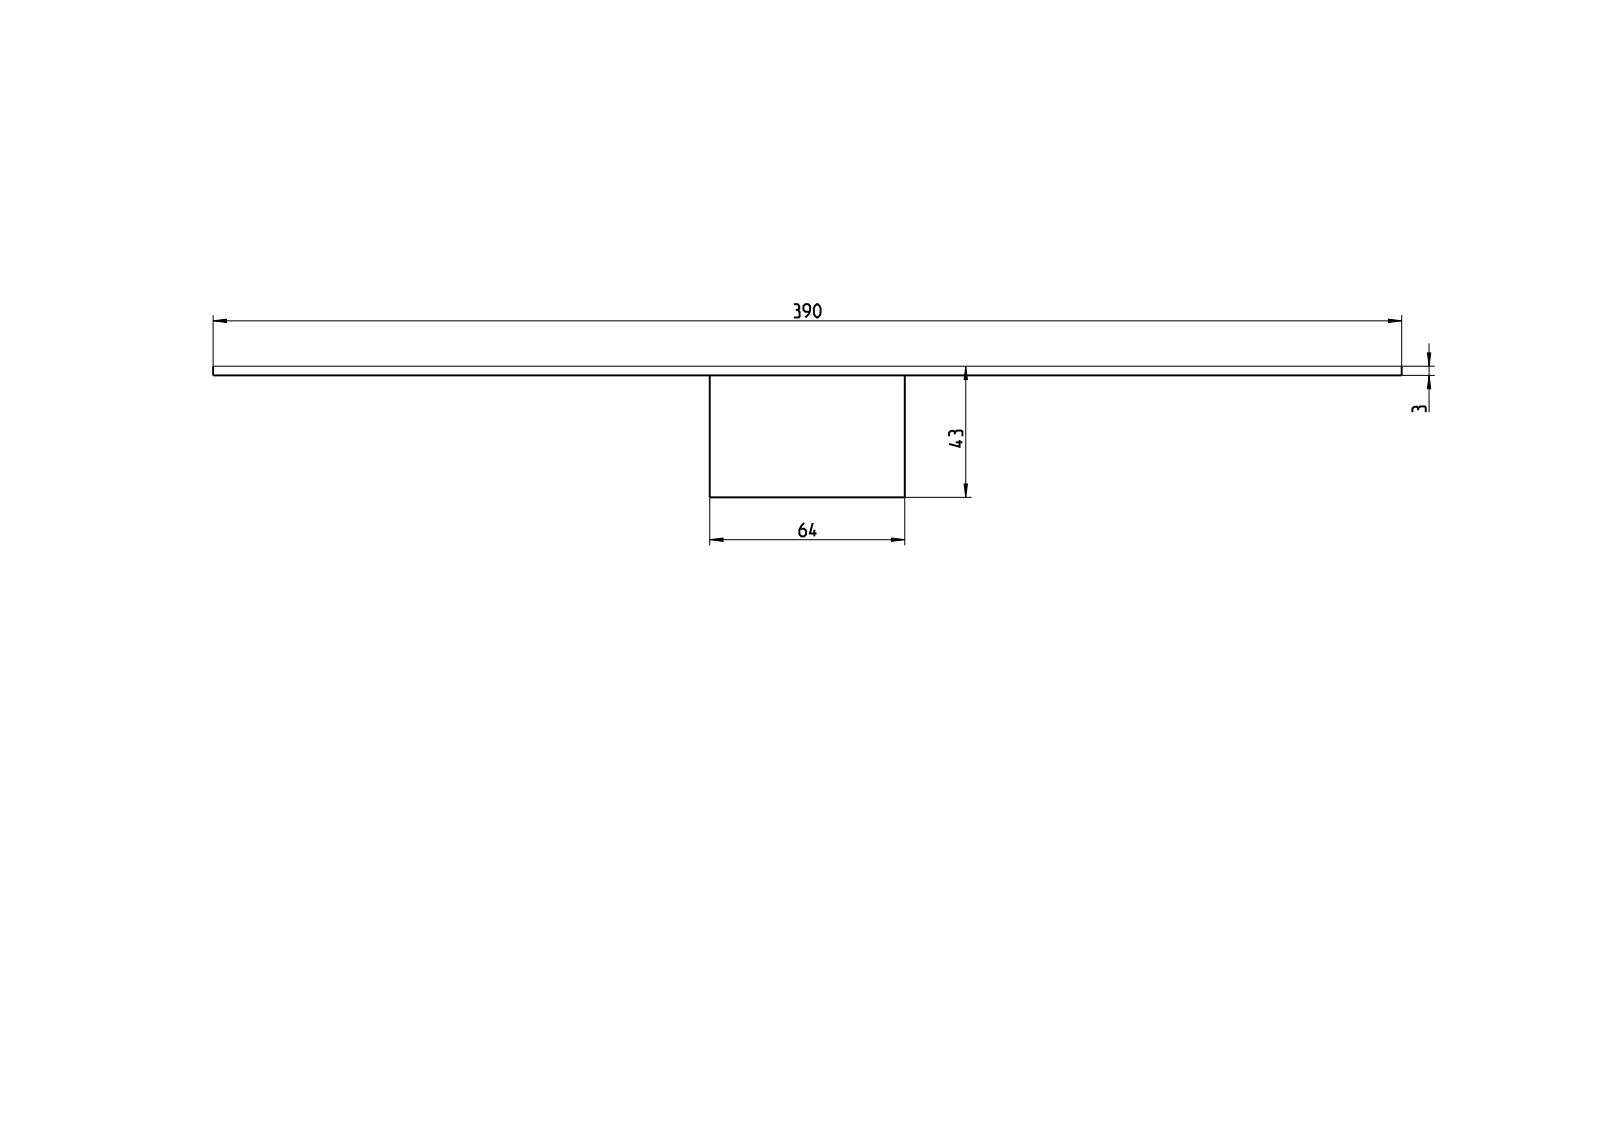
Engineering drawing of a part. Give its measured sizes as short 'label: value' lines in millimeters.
name: T-01191; AUSLASS; BKG4002LA_ASM
written by: CREO PARAMETRIC BY PTC INC, 2022024 (AUTOMOTIVE_DESIGN)
unit: mm
bodies: 2 solids, 16 faces (16 planar, 0 cylindrical, 0 other)
size: 499 × 390 × 43
volume: 678 436 mm³; area: 403 388 mm²
face distances: 3, 37, 40, 43, 64, 162.95, 226.95, 390, 227.05, 163.05
